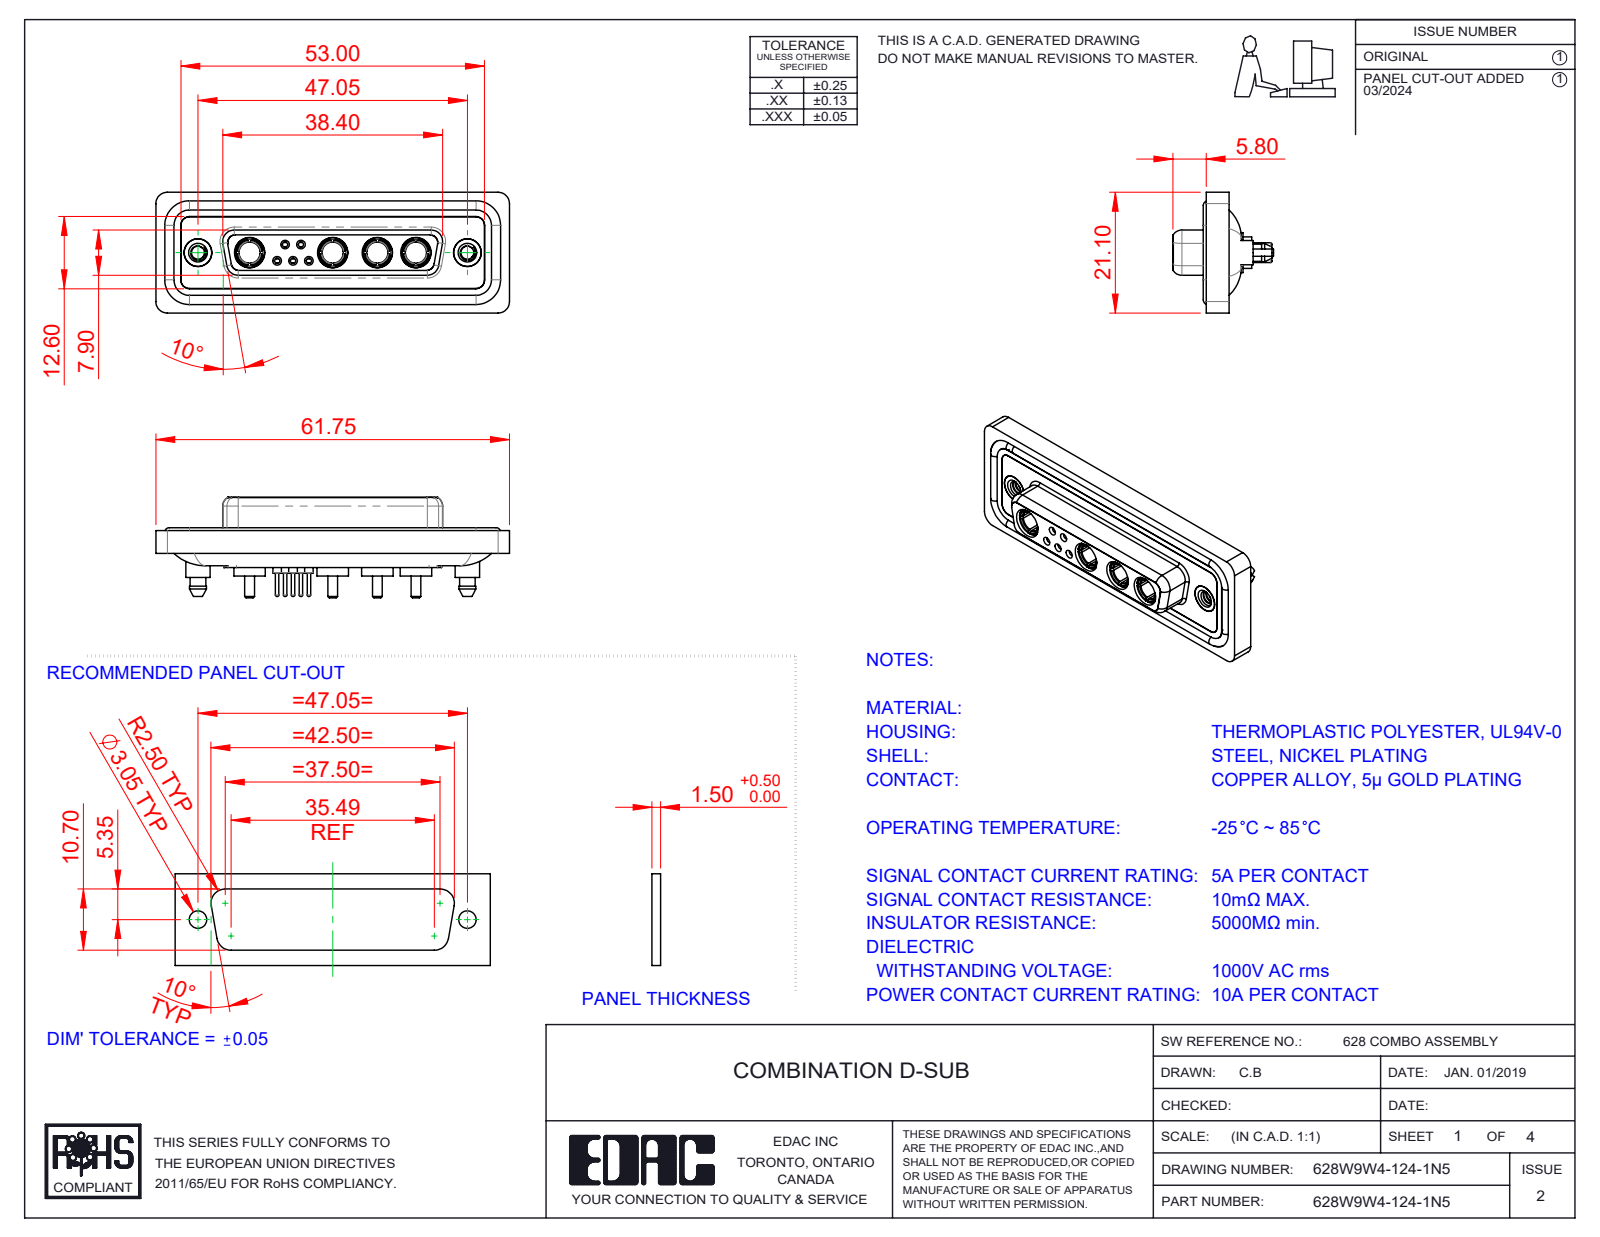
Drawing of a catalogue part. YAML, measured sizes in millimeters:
part_name: "628Combo Waterproof Housing_25 Contacts; 628Combo Contact Row 1_24; 628Combo Shell Rear_25 Contacts; 628W9W4-124-1N5 (+5 more)"
step_written_by: "SolidWorks 2023 (CONFIG_CONTROL_DESIGN)"
units: millimeters
bodies: {solids: 20, faces: 1007, planar: 312, cylindrical: 407, other: 288}
overall_size: [61.75, 21.1, 17.55]
volume: 8298
surface_area: 13844
round_holes:
  - {diameter: 4.85, count: 6}
  - {diameter: 0.9, count: 5}
  - {diameter: 1.1, count: 5}
  - {diameter: 1.5, count: 5}
  - {diameter: 2, count: 5}
  - {diameter: 3.7, count: 4}
  - {diameter: 5.3, count: 4}
  - {diameter: 1.6, count: 3}
  - {diameter: 1.7, count: 2}
  - {diameter: 2.26, count: 2}
  - {diameter: 4, count: 2}
  - {diameter: 4.05, count: 2}
round_bosses_or_shafts:
  - {diameter: 1.6, count: 6}
  - {diameter: 2.2, count: 5}
  - {diameter: 0.6, count: 5}
  - {diameter: 5.5, count: 4}
  - {diameter: 5.2, count: 4}
  - {diameter: 4.96, count: 4}
  - {diameter: 4.75, count: 4}
  - {diameter: 3.75, count: 4}
partial_cylinders:
  - {radius: 1.5, count: 24}
  - {radius: 2, count: 18}
  - {radius: 1.6, count: 10}
  - {radius: 1.35, count: 8}
  - {radius: 0.25, count: 4}
  - {radius: 0.5, count: 4}
  - {radius: 0.6, count: 4}
  - {radius: 0.65, count: 4}
face_to_face_distances: [0.4, 1.8, 7.45, 5.65, 0.5, 7.05, 6.6, 1.6, 1.1, 2.9]
hole_center_spacings: [3.16, 2.77, 5.03, 2.76, 4.4, 5.02, 5.54, 5.73]
